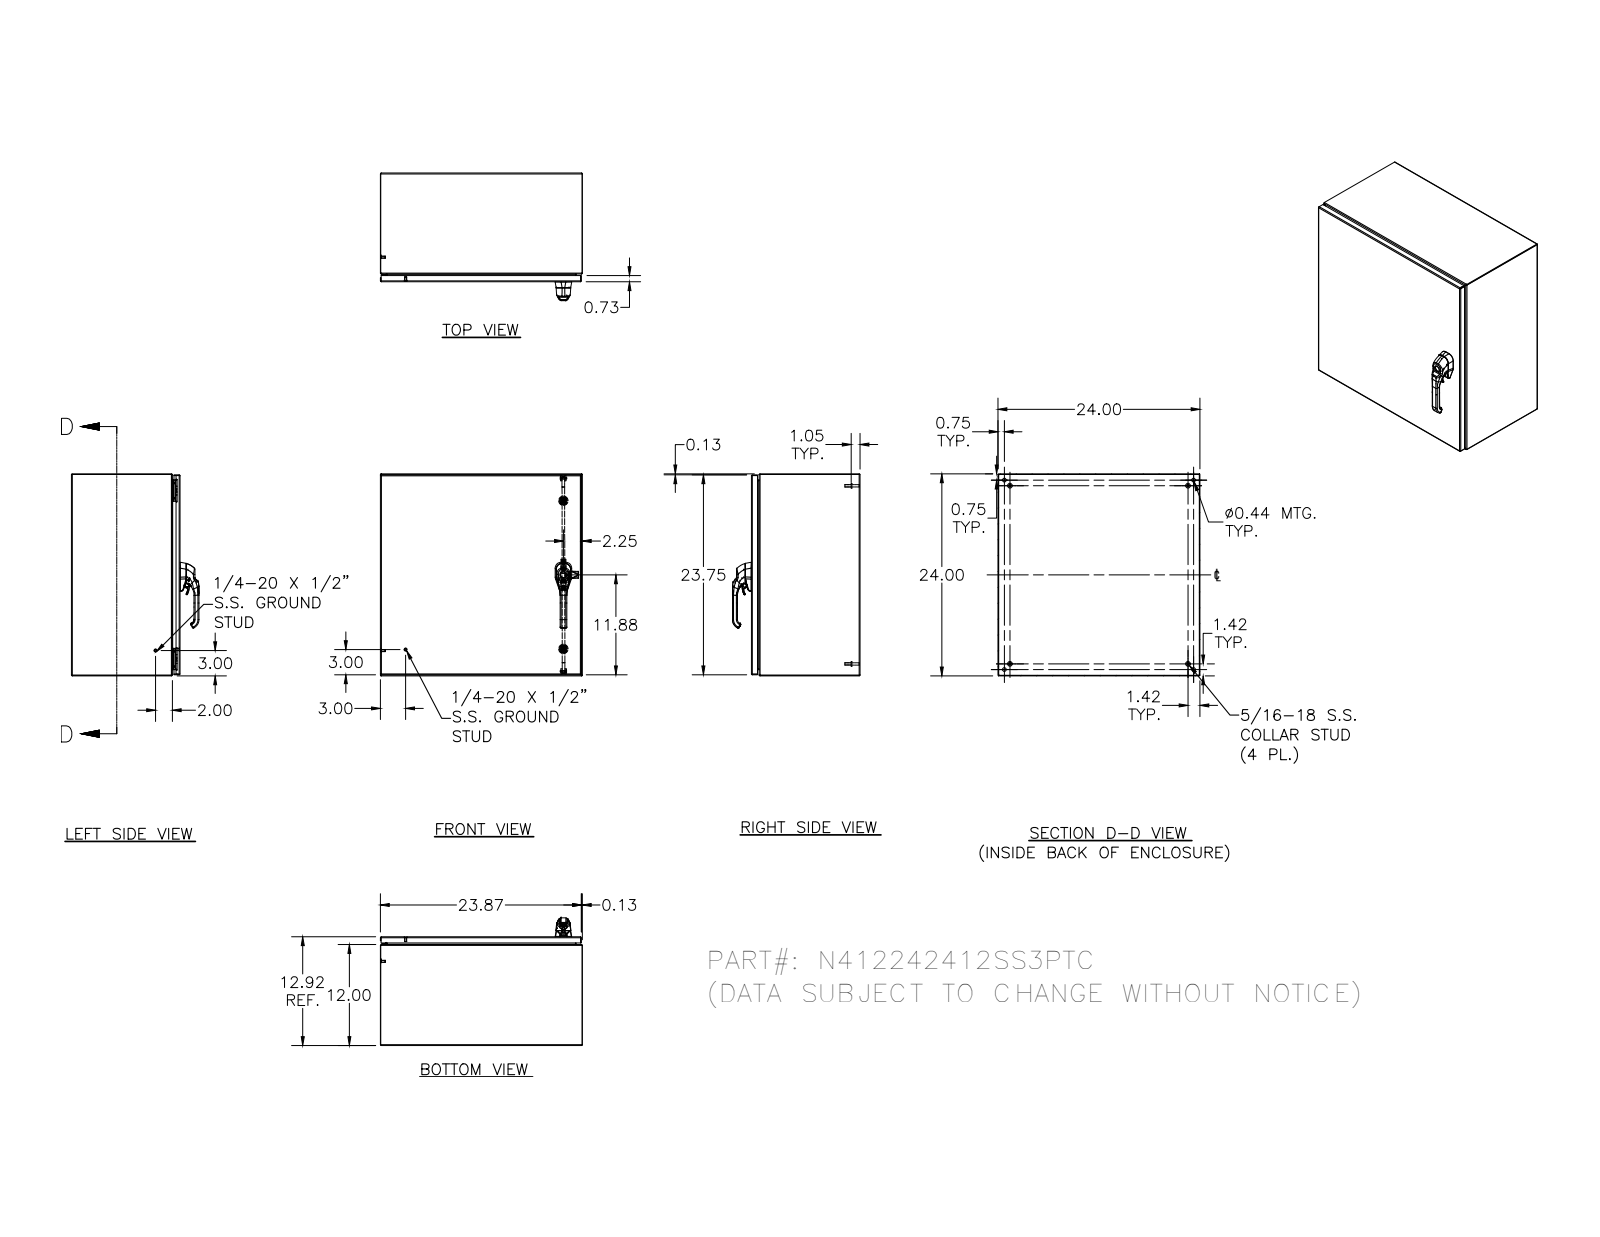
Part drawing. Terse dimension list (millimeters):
name: N412242412SS3PTC; N412242412SS3PTCBKP; N4122424SS3PTCLID; HFW328176 (+8 more)
written by: Autodesk Inventor 2011 (AUTOMOTIVE_DESIGN)
unit: mm
bodies: 63 solids, 3086 faces (1046 planar, 1117 cylindrical, 923 other)
size: 609.6 × 609.6 × 385.2
volume: 3 197 000 mm³; area: 3 325 000 mm²
holes: 5× ⌀4.2, 4× ⌀2.4, 4× ⌀3.9, 4× ⌀4.2, 4× ⌀4.4, 4× ⌀4.8, 4× ⌀5, 4× ⌀11.1, 3× ⌀5.4, 2× ⌀2.7, 2× ⌀4, 2× ⌀4.1
bosses: 10× ⌀6.4, 6× ⌀6, 5× ⌀15, 4× ⌀14.3, 4× ⌀9.1, 4× ⌀8.1, 4× ⌀7.9, 4× ⌀7.6
rounds: 180× R0.5, 101× R0.3, 30× R0.8, 26× R1.3, 23× R3, 21× R0.5, 20× R2.7, 18× R0.4
face distances: 1.9, 607.7, 326.2, 605.8, 609.6, 328.1, 324.3, 302.9, 23.3, 18.8
hole spacings: 507.9, 571.5, 580.9, 0.4, 16.8, 41.1, 524.7, 594.8
